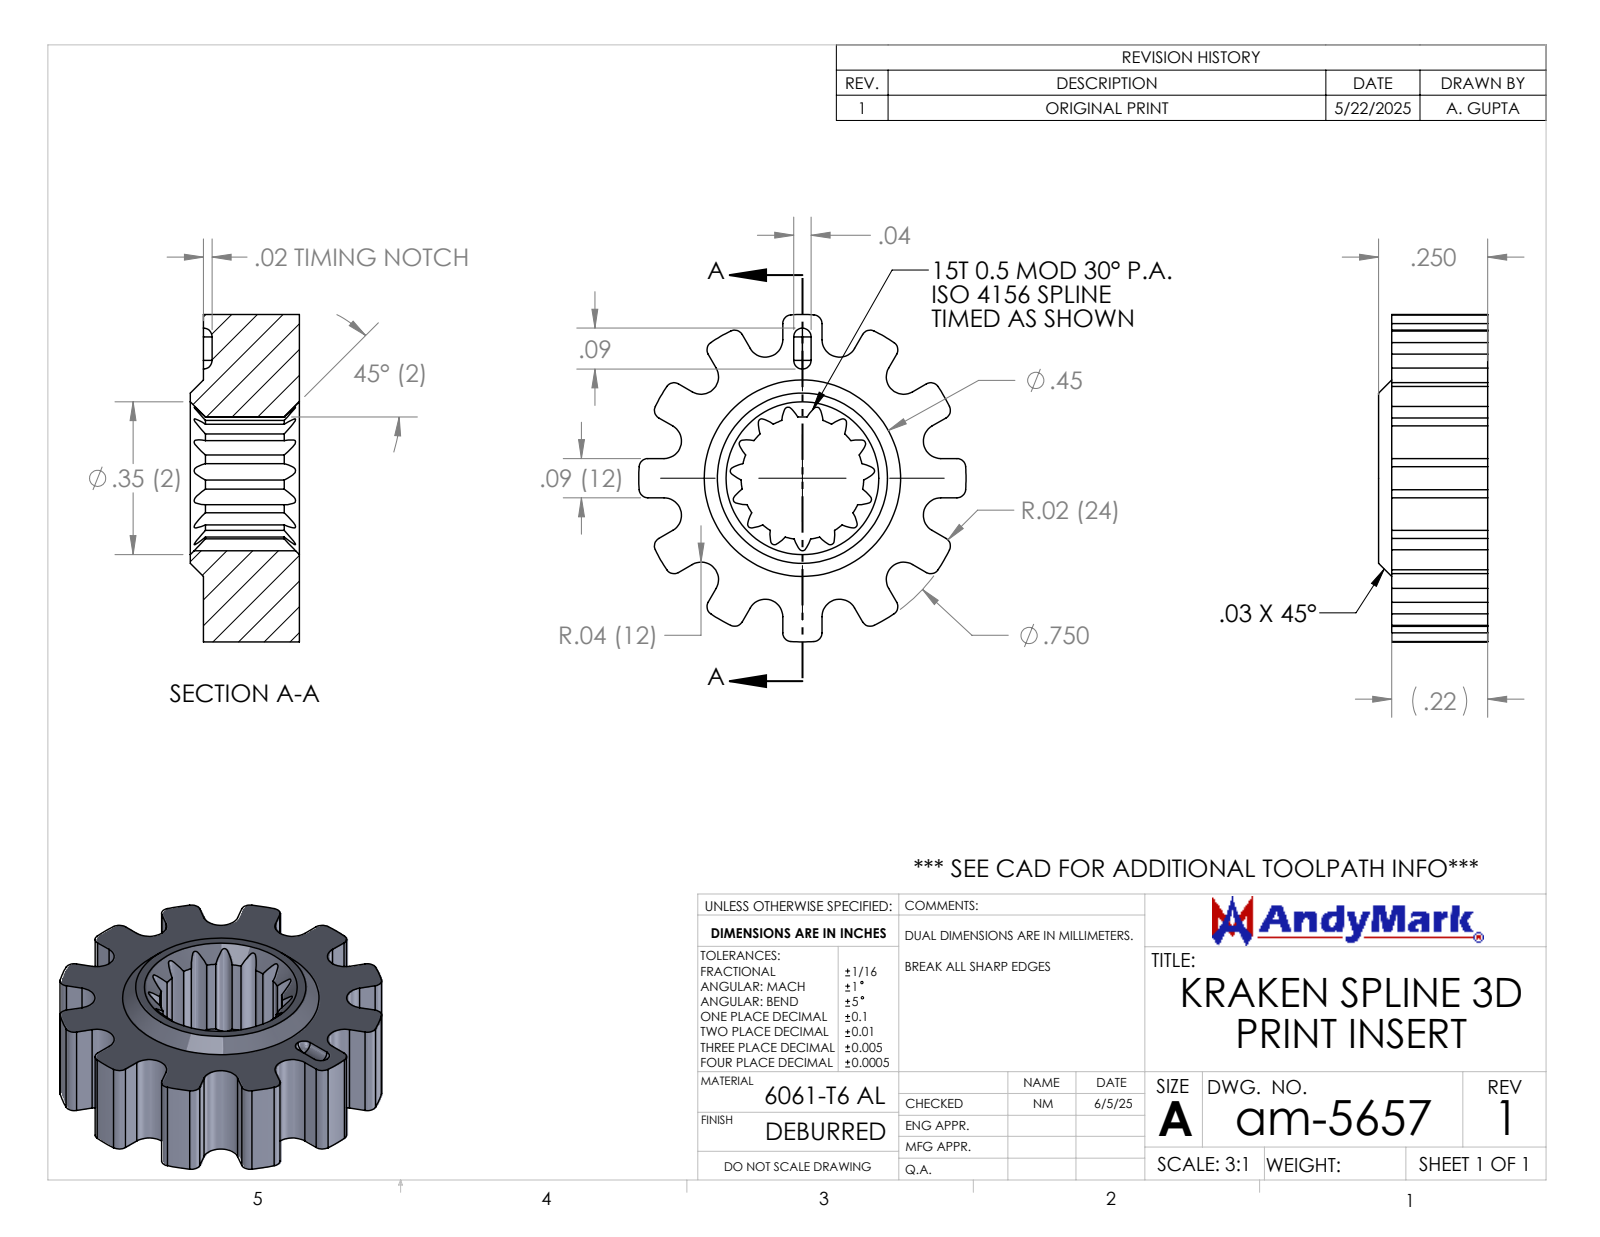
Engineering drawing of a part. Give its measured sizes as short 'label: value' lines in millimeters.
name: am-5657 Kraken Spline 3D Print Insert
written by: SolidWorks 2024 (AUTOMOTIVE_DESIGN)
unit: mm
bodies: 1 solid, 126 faces (27 planar, 74 cylindrical, 25 other)
size: 19.1 × 19.1 × 6.4
volume: 1 000 mm³; area: 1 068 mm²
rounds: 25× R0.5, 12× R1, 1× R3.6, 1× R9.5
face distances: 5.6, 2.3, 6.4, 0.8
